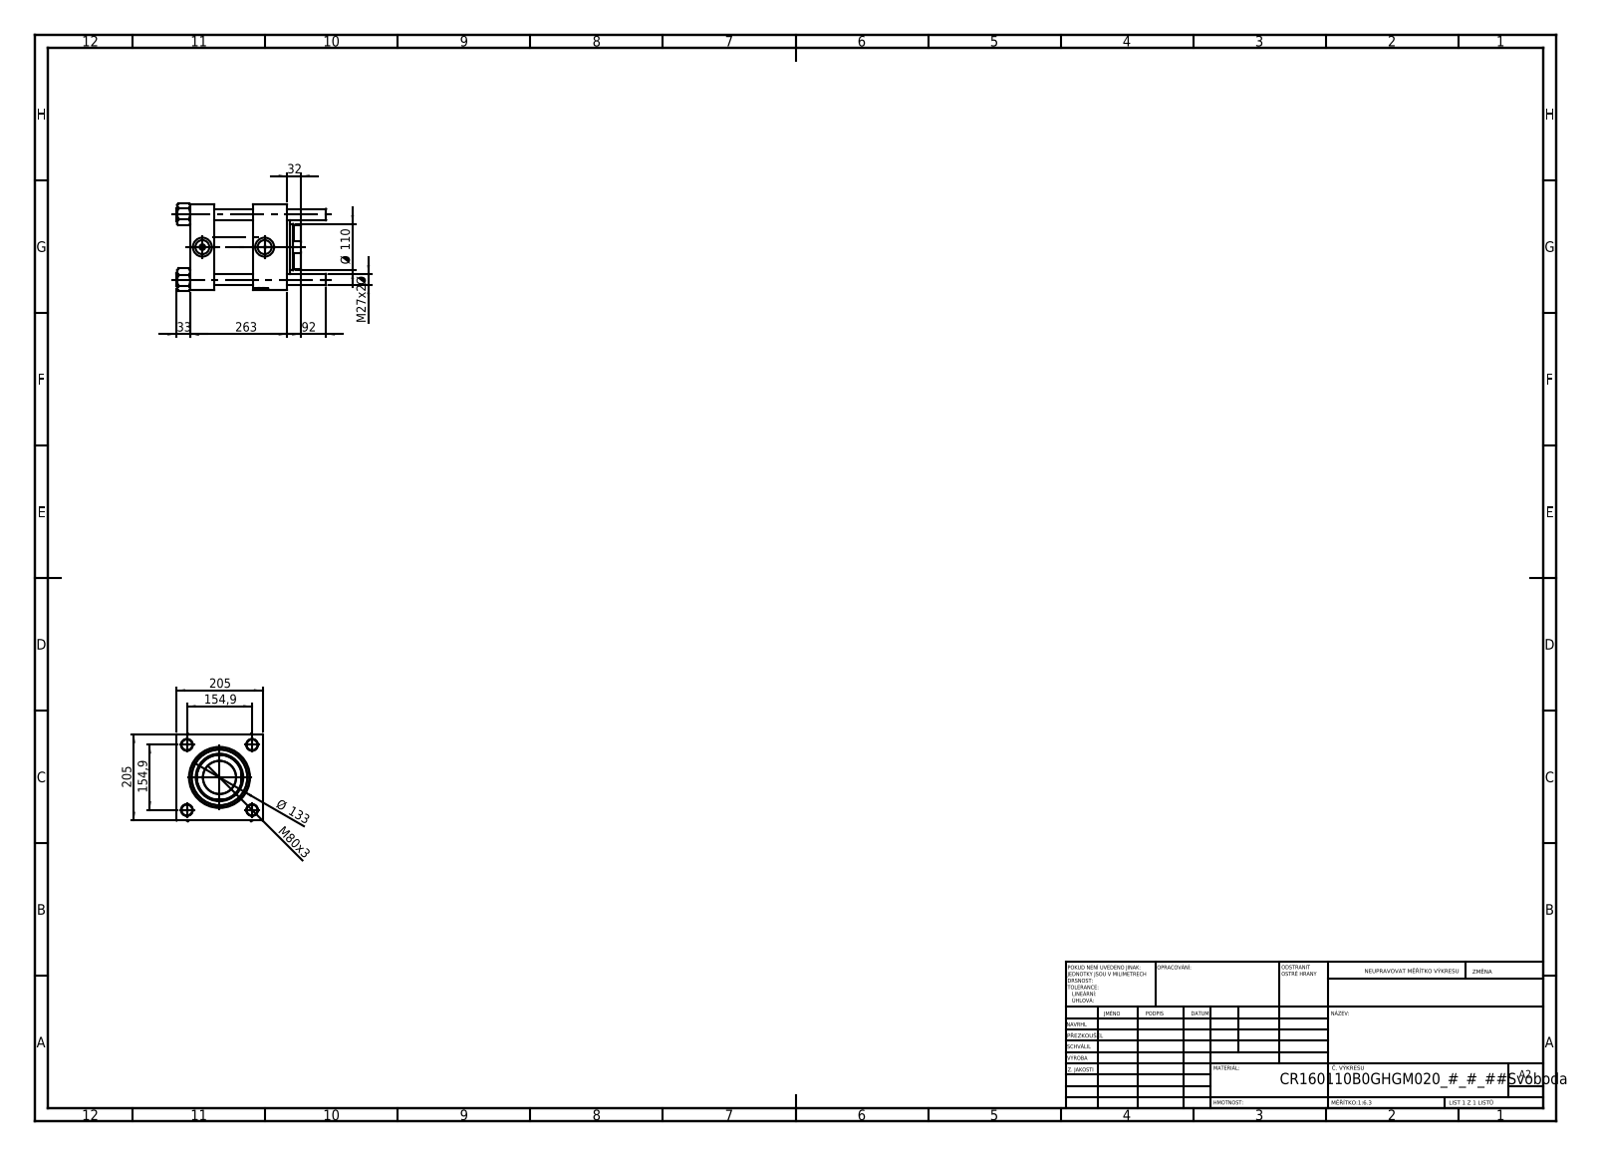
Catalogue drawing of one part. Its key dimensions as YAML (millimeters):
part_name: "V215CR_VCP_B; V215CR_B-1; V215_VC_A; NUT_M5_B (+1 more)"
step_written_by: "SolidWorks 2019 (CONFIG_CONTROL_DESIGN)"
units: millimeters
bodies: {solids: 11, faces: 1206, planar: 480, cylindrical: 78, other: 648}
overall_size: [356, 207.94, 205]
volume: 7956000
surface_area: 779822
round_holes:
  - {diameter: 27, count: 4}
  - {diameter: 7, count: 2}
  - {diameter: 33.24, count: 2}
  - {diameter: 45, count: 2}
  - {diameter: 78.5, count: 1}
  - {diameter: 110, count: 1}
  - {diameter: 113, count: 1}
  - {diameter: 120, count: 1}
  - {diameter: 142, count: 1}
  - {diameter: 160, count: 1}
round_bosses_or_shafts:
  - {diameter: 30, count: 4}
  - {diameter: 166, count: 1}
  - {diameter: 133, count: 1}
partial_cylinders:
  - {radius: 54, count: 1}
face_to_face_distances: [205, 58, 92, 173, 150, 231, 81, 202.3, 144.3, 52.3]
hole_center_spacings: [109.53, 154.9, 219.06, 148]
